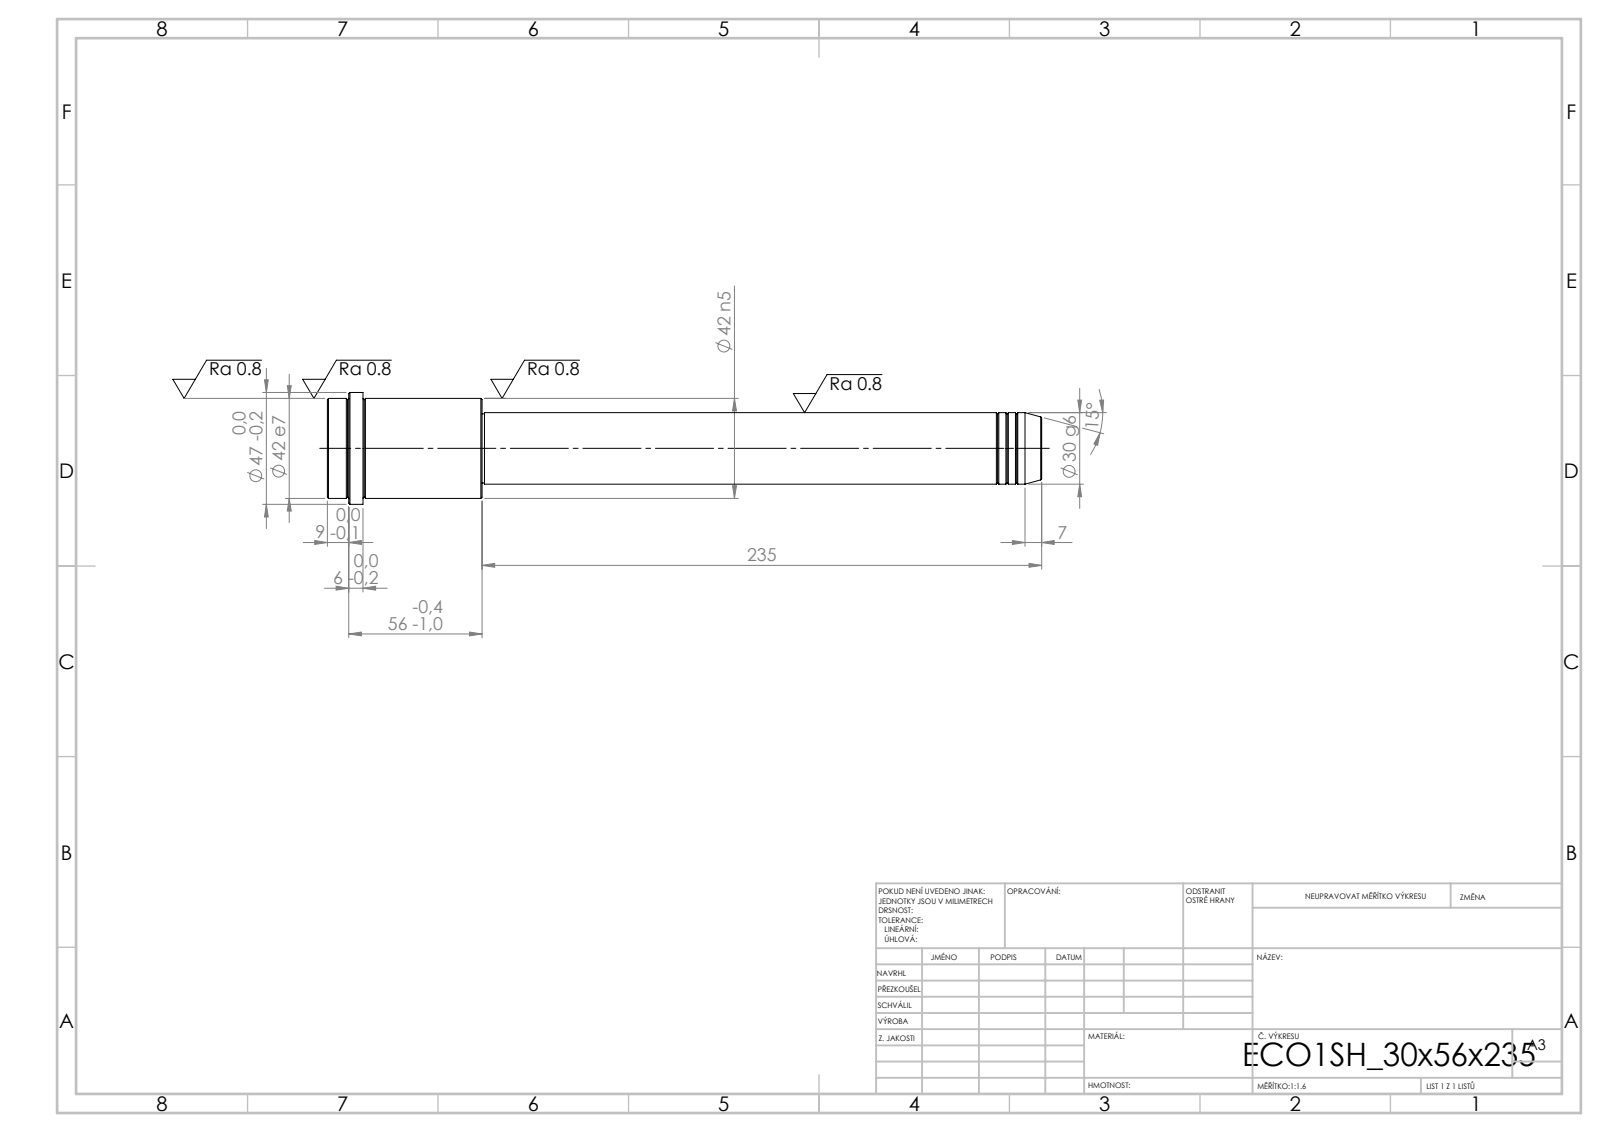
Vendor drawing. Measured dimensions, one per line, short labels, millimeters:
written by: SolidWorks 2019 (CONFIG_CONTROL_DESIGN)
unit: mm
bodies: 1 solid, 52 faces (6 planar, 16 cylindrical, 30 other)
size: 300 × 47 × 47
volume: 257 358 mm³; area: 34 359 mm²
bosses: 1× ⌀47, 1× ⌀42, 1× ⌀30, 1× ⌀29
face distances: 65, 235, 300, 285, 50, 15, 291, 56, 6, 9
